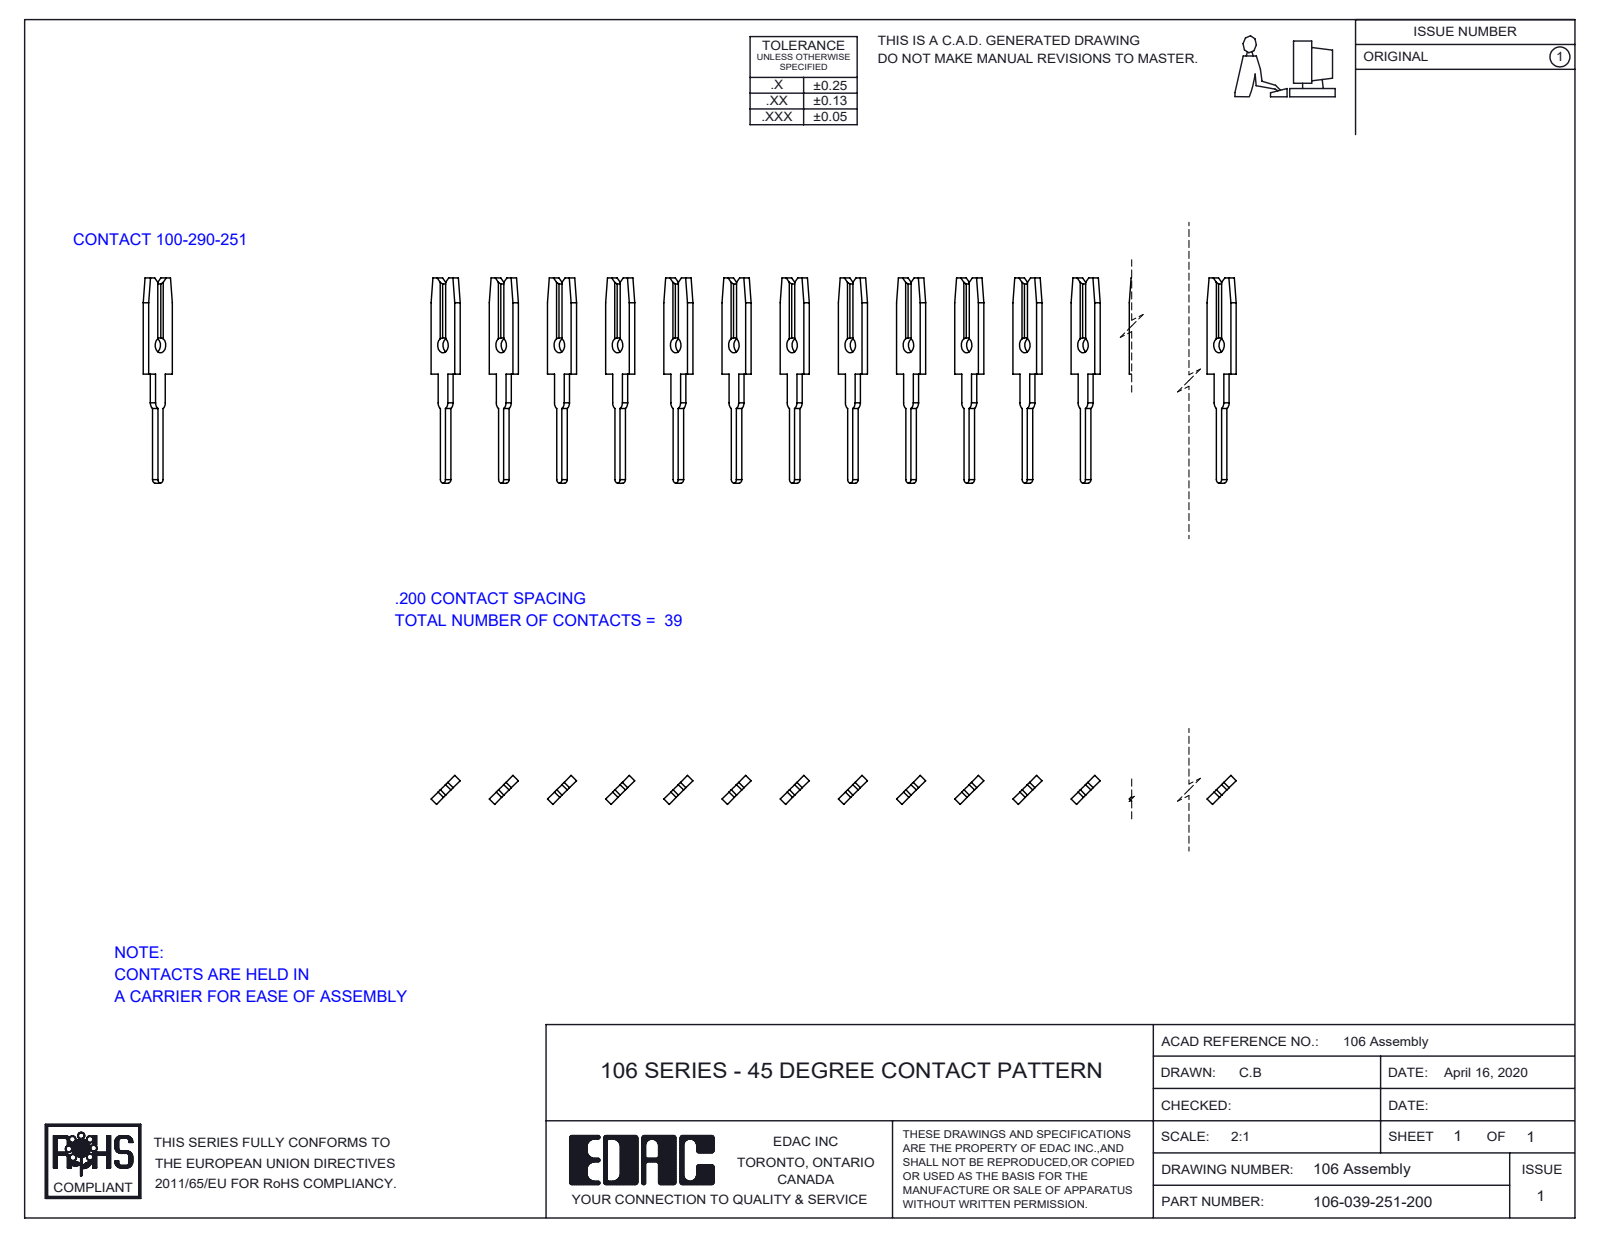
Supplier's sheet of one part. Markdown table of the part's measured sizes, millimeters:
| quantity | value |
| --- | --- |
| part name | 100-290-001_100-290-251; 106-039-251-200 |
| STEP written by | SolidWorks 2016 (CONFIG_CONTROL_DESIGN) |
| units | millimeters |
| bodies | 39 solids, 1092 faces (858 planar, 234 cylindrical, 0 other) |
| overall size | 195.6 × 17.9 × 2.5 |
| volume | 720 mm³ |
| surface area | 3 505 mm² |
| round holes (diameter × count) | 1.3 × 39 |
| partial cylindrical surfaces (radius × count) | 0.3 × 39, 0.6 × 39 |
| main face-to-face distances | 3.6, 21.5, 18, 7.2, 25.1, 14.4, 10.8, 28.7, 10.8, 39.5 |
| hole center spacings | 3.6, 7.2, 10.8, 21.5, 46.7, 25.1, 39.5, 43.1 |
